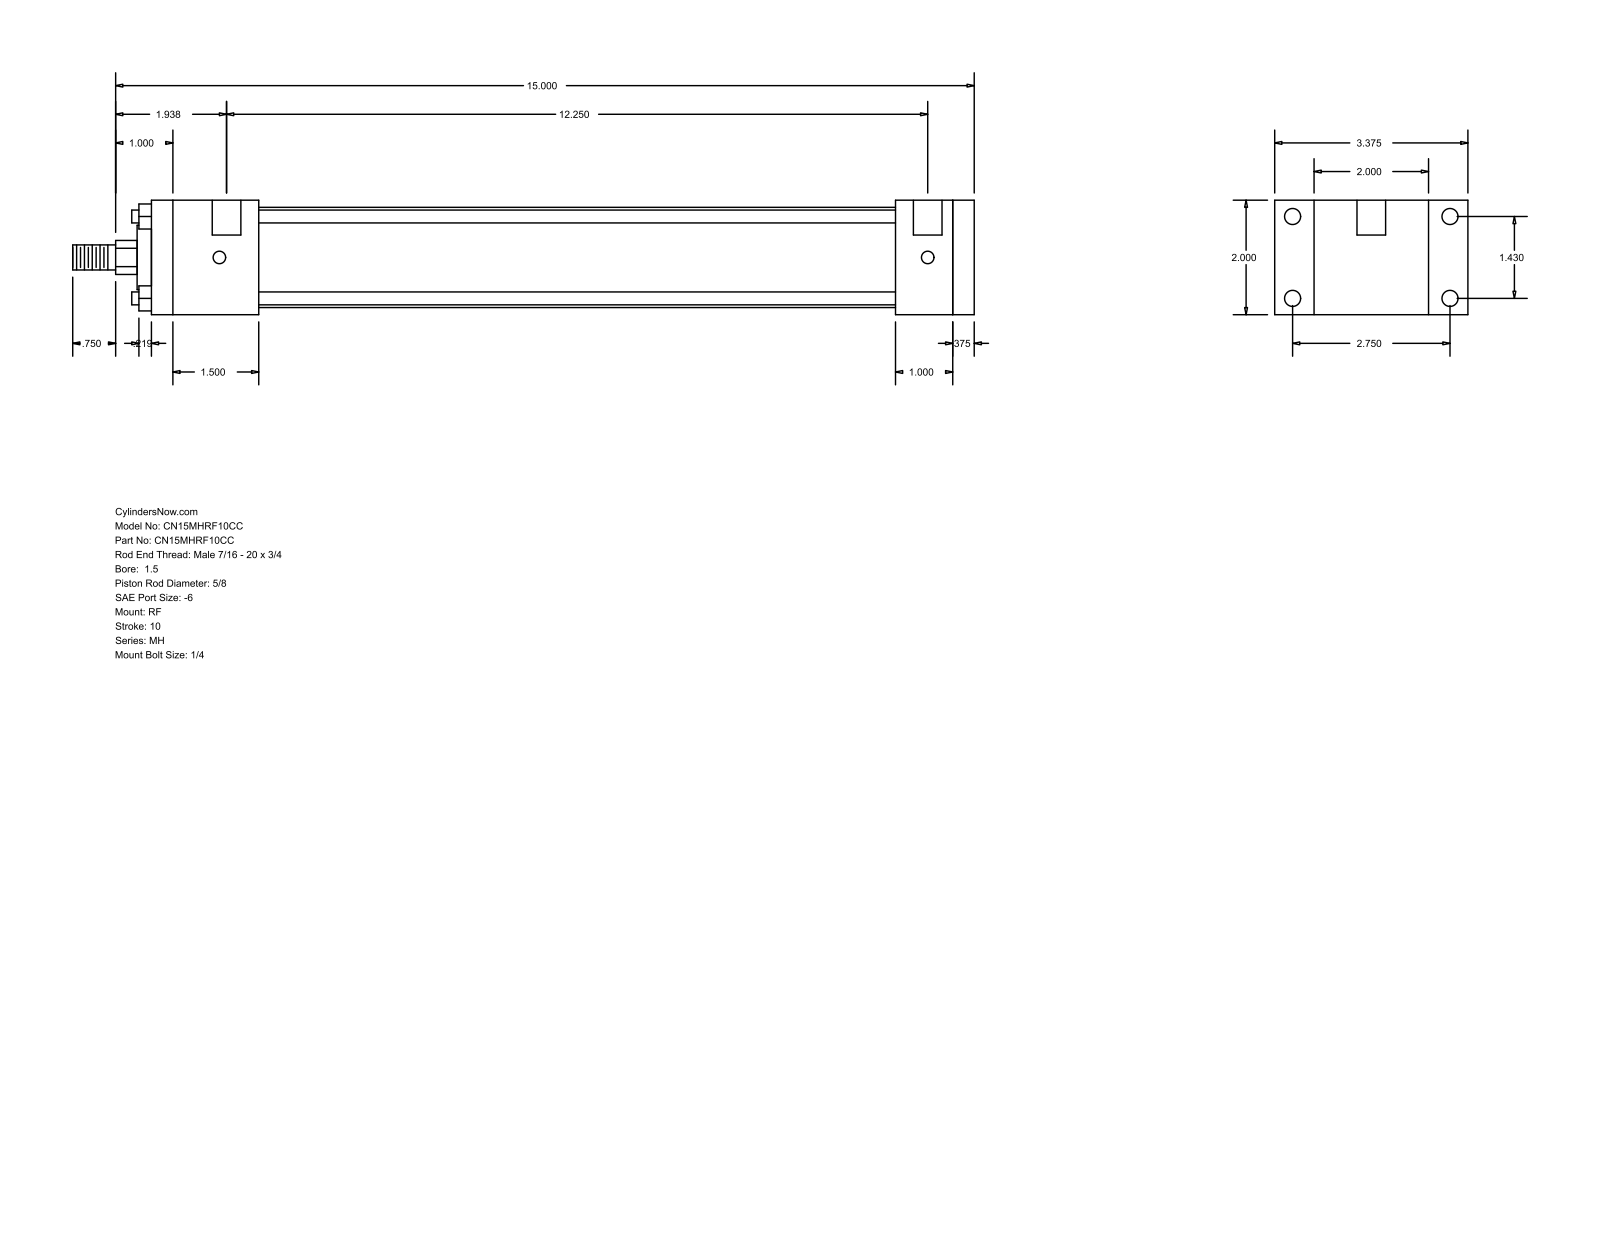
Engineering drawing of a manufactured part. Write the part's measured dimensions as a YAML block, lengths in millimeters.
part_name: "MH_RF__0150_0.625"
step_written_by: "GSSL Pune (CONFIG_CONTROL_DESIGN)"
units: millimeters
bodies: {solids: 0, faces: 92, planar: 64, cylindrical: 28, other: 0}
overall_size: [400.05, 85.72, 50.8]
round_holes:
  - {diameter: 5.56, count: 4}
  - {diameter: 7.14, count: 4}
  - {diameter: 12.7, count: 2}
round_bosses_or_shafts:
  - {diameter: 5.71, count: 4}
  - {diameter: 44.45, count: 1}
  - {diameter: 28.57, count: 1}
  - {diameter: 15.88, count: 1}
  - {diameter: 11.11, count: 1}
partial_cylinders:
  - {radius: 7.54, count: 1}
face_to_face_distances: [50.8, 9.52, 365.12, 355.6, 34.93, 17.46, 68.26, 330.19, 25.41, 47.62]
hole_center_spacings: [36.32, 69.84, 78.72, 314.32, 3.17, 311.15]
